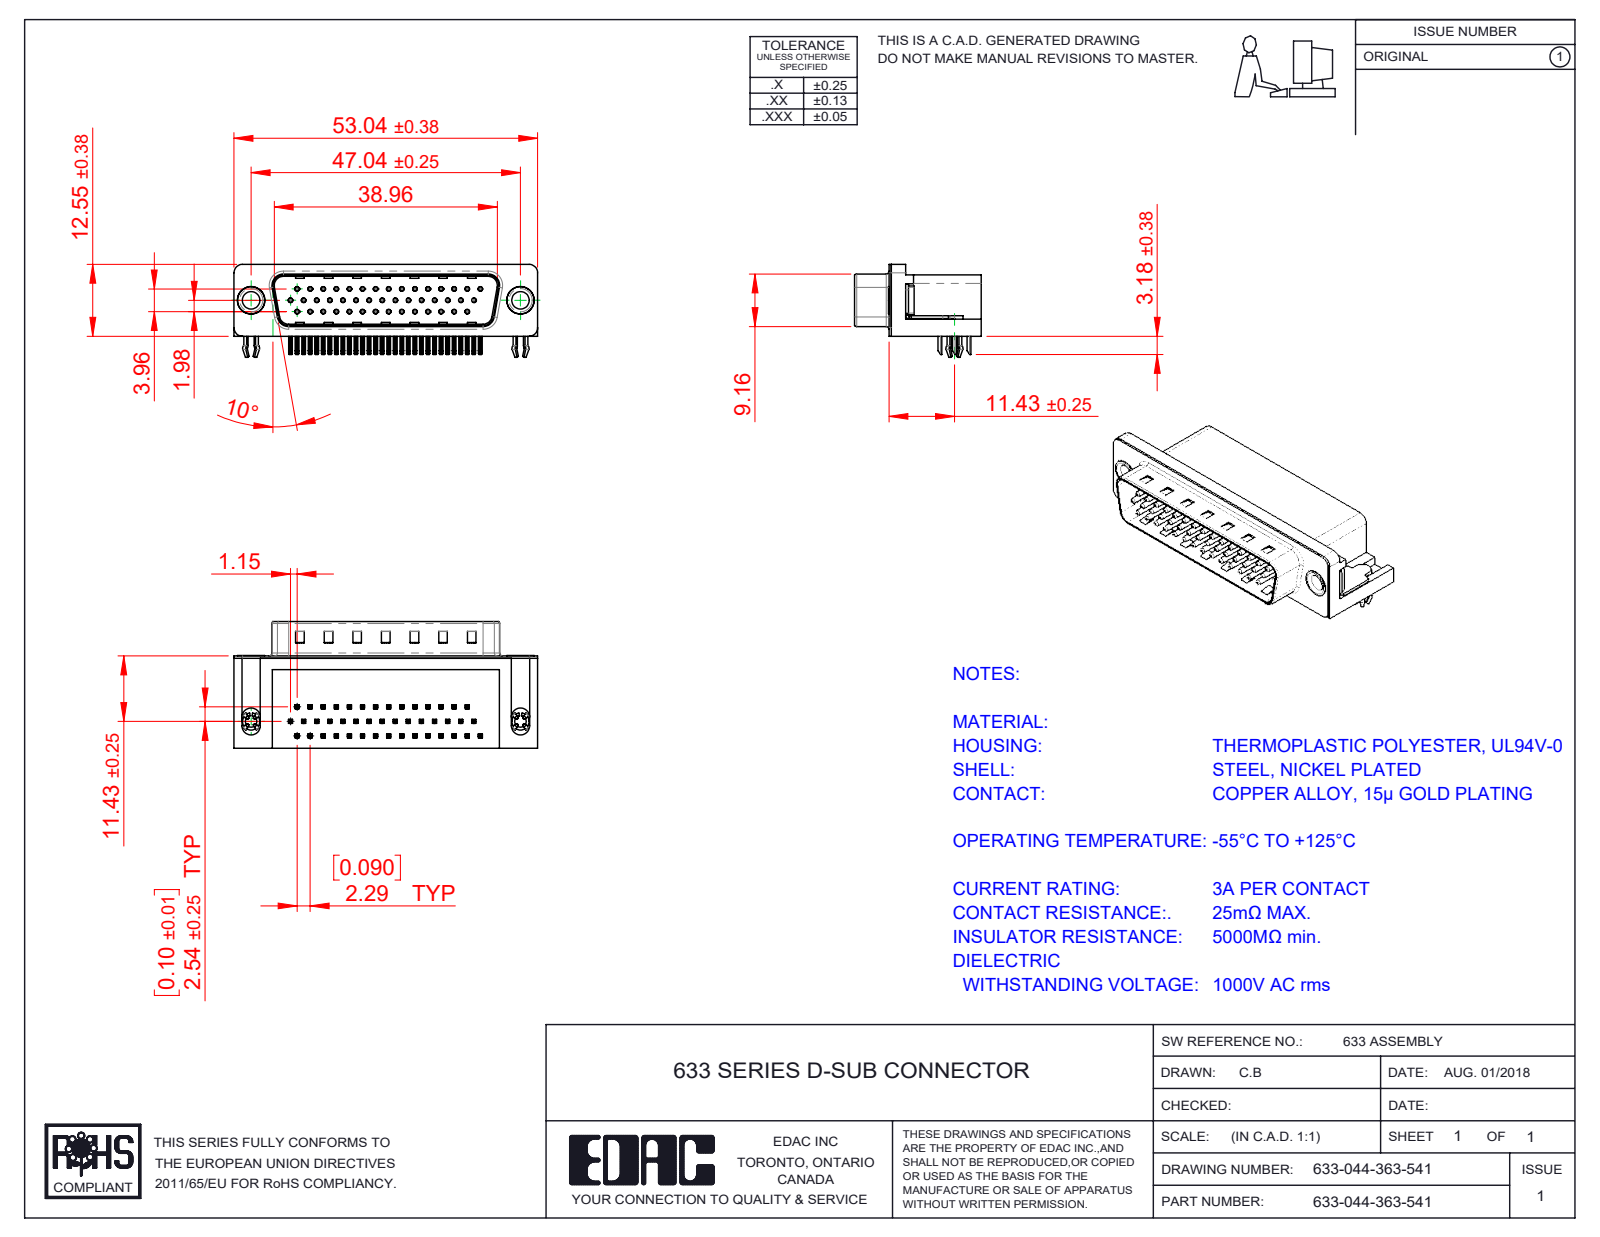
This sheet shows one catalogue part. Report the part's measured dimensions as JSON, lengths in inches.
{"part_name": "633 Contact Top; 633 Contact Middle; 633 Contact Bottom; 633 4 Prong Board Lock (+4 more)", "step_written_by": "SolidWorks 2016 (CONFIG_CONTROL_DESIGN)", "units": "inches", "bodies": {"solids": 50, "faces": 3770, "planar": 2359, "cylindrical": 1048, "other": 363}, "overall_size": [2.088, 0.87, 0.64], "volume_in3": 0.495, "surface_area_in2": 15.92, "round_holes": [[0.014, 44], [0.031, 44], [0.079, 2], [0.12, 2], [0.157, 2], [0.189, 2], [0.197, 2]], "round_bosses_or_shafts": [[0.03, 44], [0.193, 2], [0.187, 2], [0.152, 2], [0.118, 2]], "partial_cylinders_radius": [[0.01, 188], [0.005, 88], [0.039, 16], [0.02, 9], [0.063, 8], [0.059, 7], [0.035, 4], [0.079, 4]], "face_to_face_distances": [0.016, 0.407, 0.618, 0.114, 0.345, 0.098, 0.083, 0.634, 0.421, 0.1], "hole_center_spacings": [0.09, 0.18, 0.18, 0.09, 0.27, 0.361, 0.451, 0.089]}
